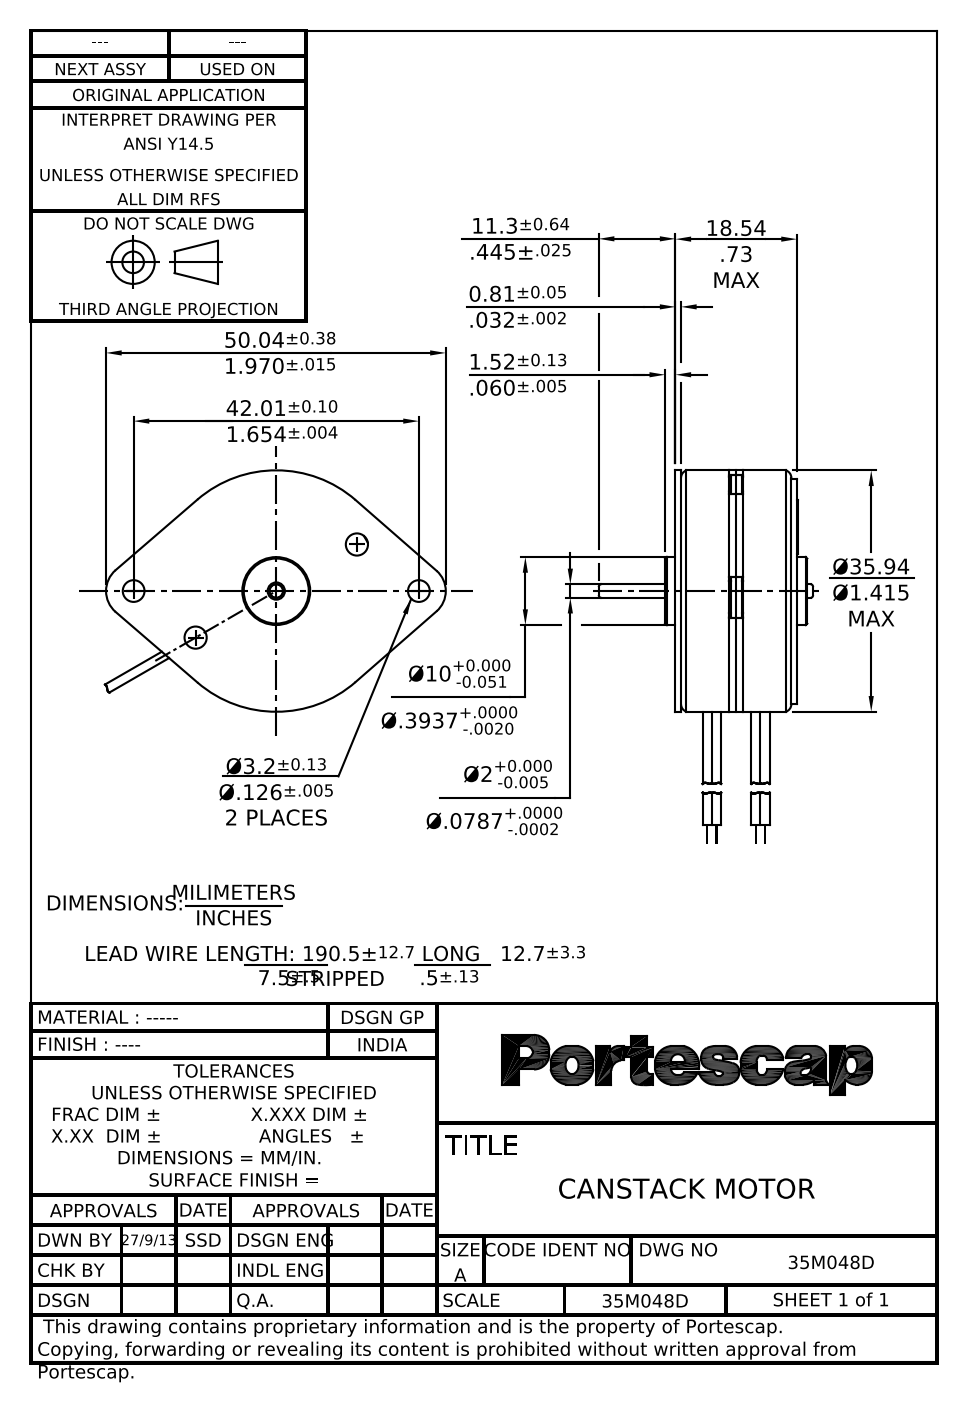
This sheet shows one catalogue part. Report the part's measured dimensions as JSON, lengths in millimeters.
{"part_name": "BREP_WITH_VOIDS_11894; MANIFOLD_SOLID_BREP_12034; BREP_WITH_VOIDS_11403_1_ASM; MANIFOLD_SOLID_BREP_11616_1 (+7 more)", "step_written_by": "PRO/ENGINEER BY PARAMETRIC TECHNOLOGY CORPORATION, 2014310 (CONFIG_CONTROL_DESIGN)", "units": "millimeters", "bodies": {"solids": 6, "faces": 411, "planar": 176, "cylindrical": 177, "other": 58}, "overall_size": [69.6, 43.6, 31.6], "volume_mm3": 17960, "surface_area_mm2": 6114, "round_holes": [[3, 6], [3.3, 6], [2.2, 3], [3, 3], [1.3, 2], [3.2, 2], [2, 1], [7.3, 1]], "round_bosses_or_shafts": [[1.3, 4], [0.8, 4], [2.9, 3], [2.4, 3], [35.7, 1], [35.5, 1], [34.1, 1], [33.1, 1]], "partial_cylinders_radius": [[1, 4], [1.4, 4], [2.2, 2], [4, 1], [4.1, 1], [17.8, 1]], "face_to_face_distances": [17.9, 0.8, 17.1, 16.3, 1.5, 1.6, 17.2, 18, 15.4, 3.1], "hole_center_spacings": [13.7, 7.1, 19.4, 23.7, 26.5, 27.4, 11.4, 18.5]}
